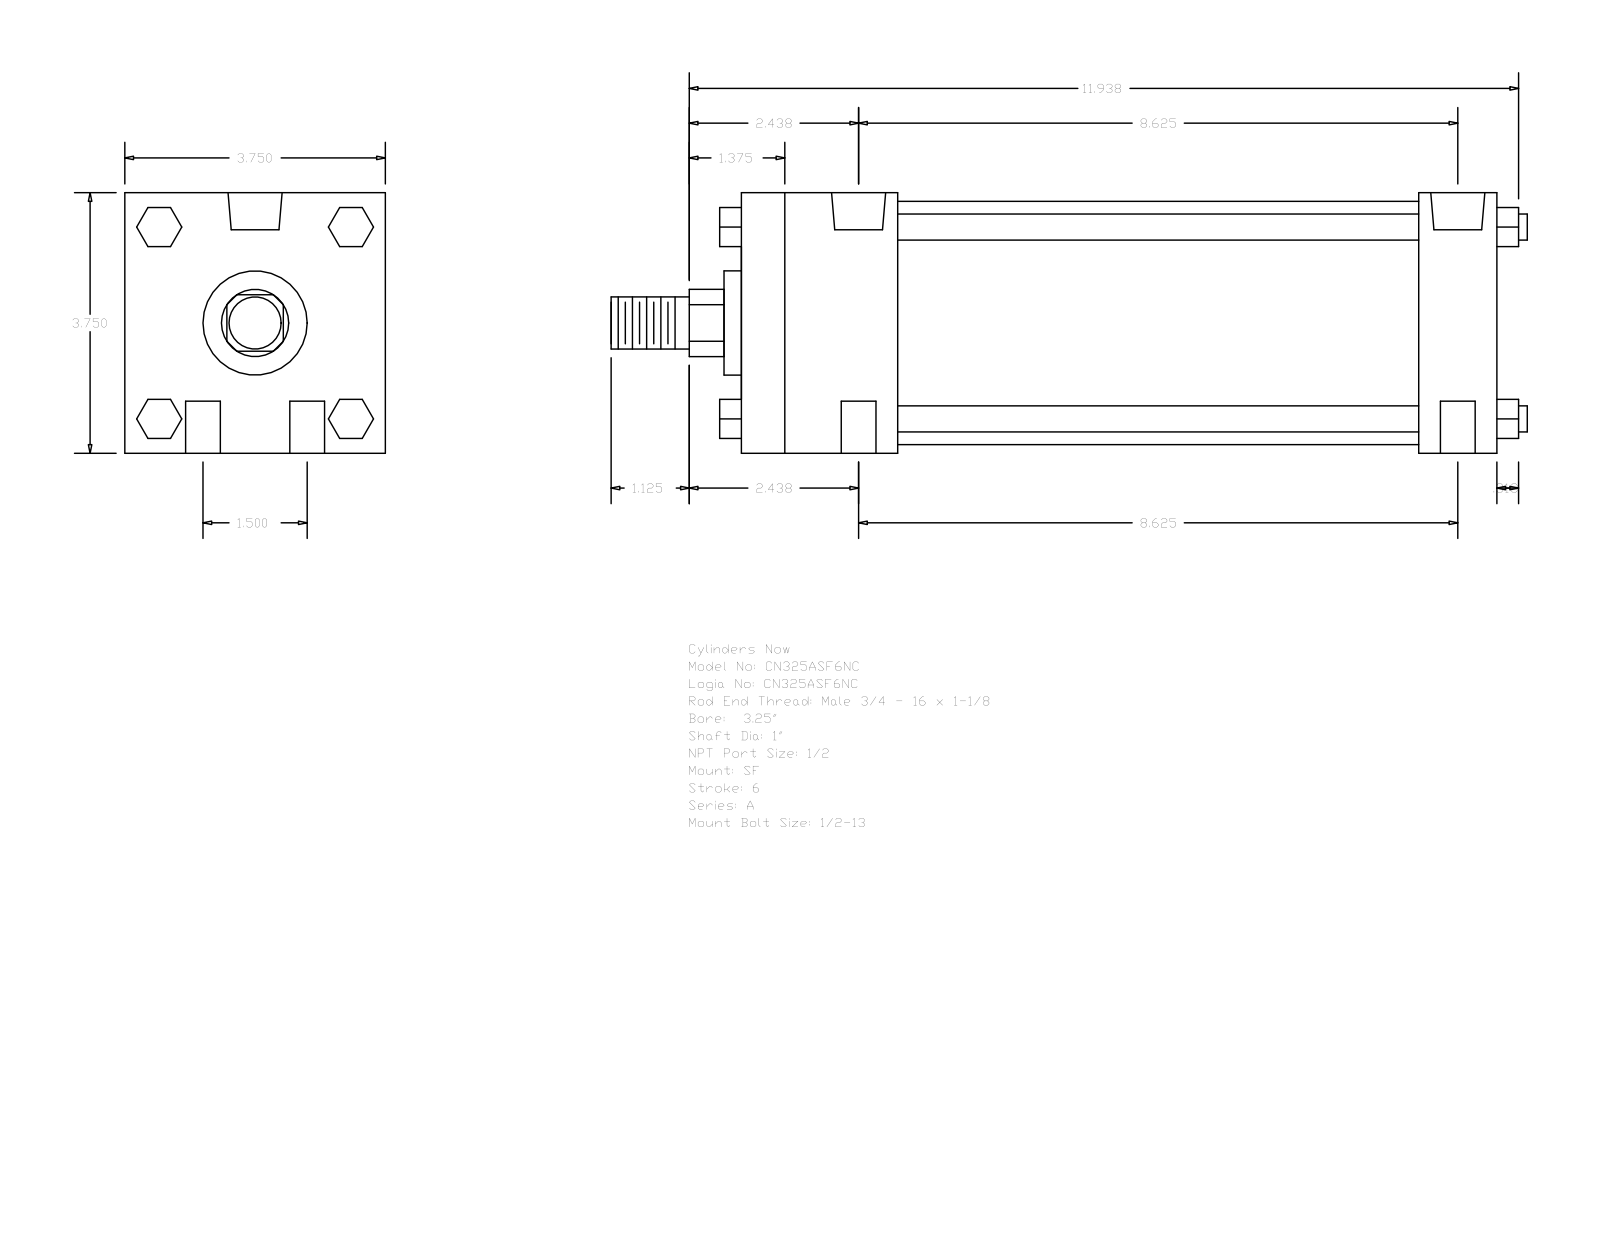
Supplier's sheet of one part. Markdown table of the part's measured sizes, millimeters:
| quantity | value |
| --- | --- |
| part name | A_SF__0325_1 |
| STEP written by | GSSL Pune (CONFIG_CONTROL_DESIGN) |
| units | millimeters |
| bodies | 0 solids, 124 faces (94 planar, 30 cylindrical, 0 other) |
| overall size | 334.96 × 95.25 × 95.25 |
| round holes (diameter × count) | 12.7 × 4, 8.73 × 2, 19.77 × 2 |
| round bosses / shafts (diameter × count) | 9.53 × 4, 88.9 × 1, 38.1 × 1, 25.4 × 1, 19.05 × 1 |
| partial cylindrical surfaces (radius × count) | 12.29 × 1 |
| main face-to-face distances | 95.24, 276.22, 28.57, 247.65, 57.15, 190.5, 219.07, 14.28, 35.05, 60.71 |
| hole center spacings | 19.05, 219.91, 219.08, 38.1, 222.37, 212.72 |
